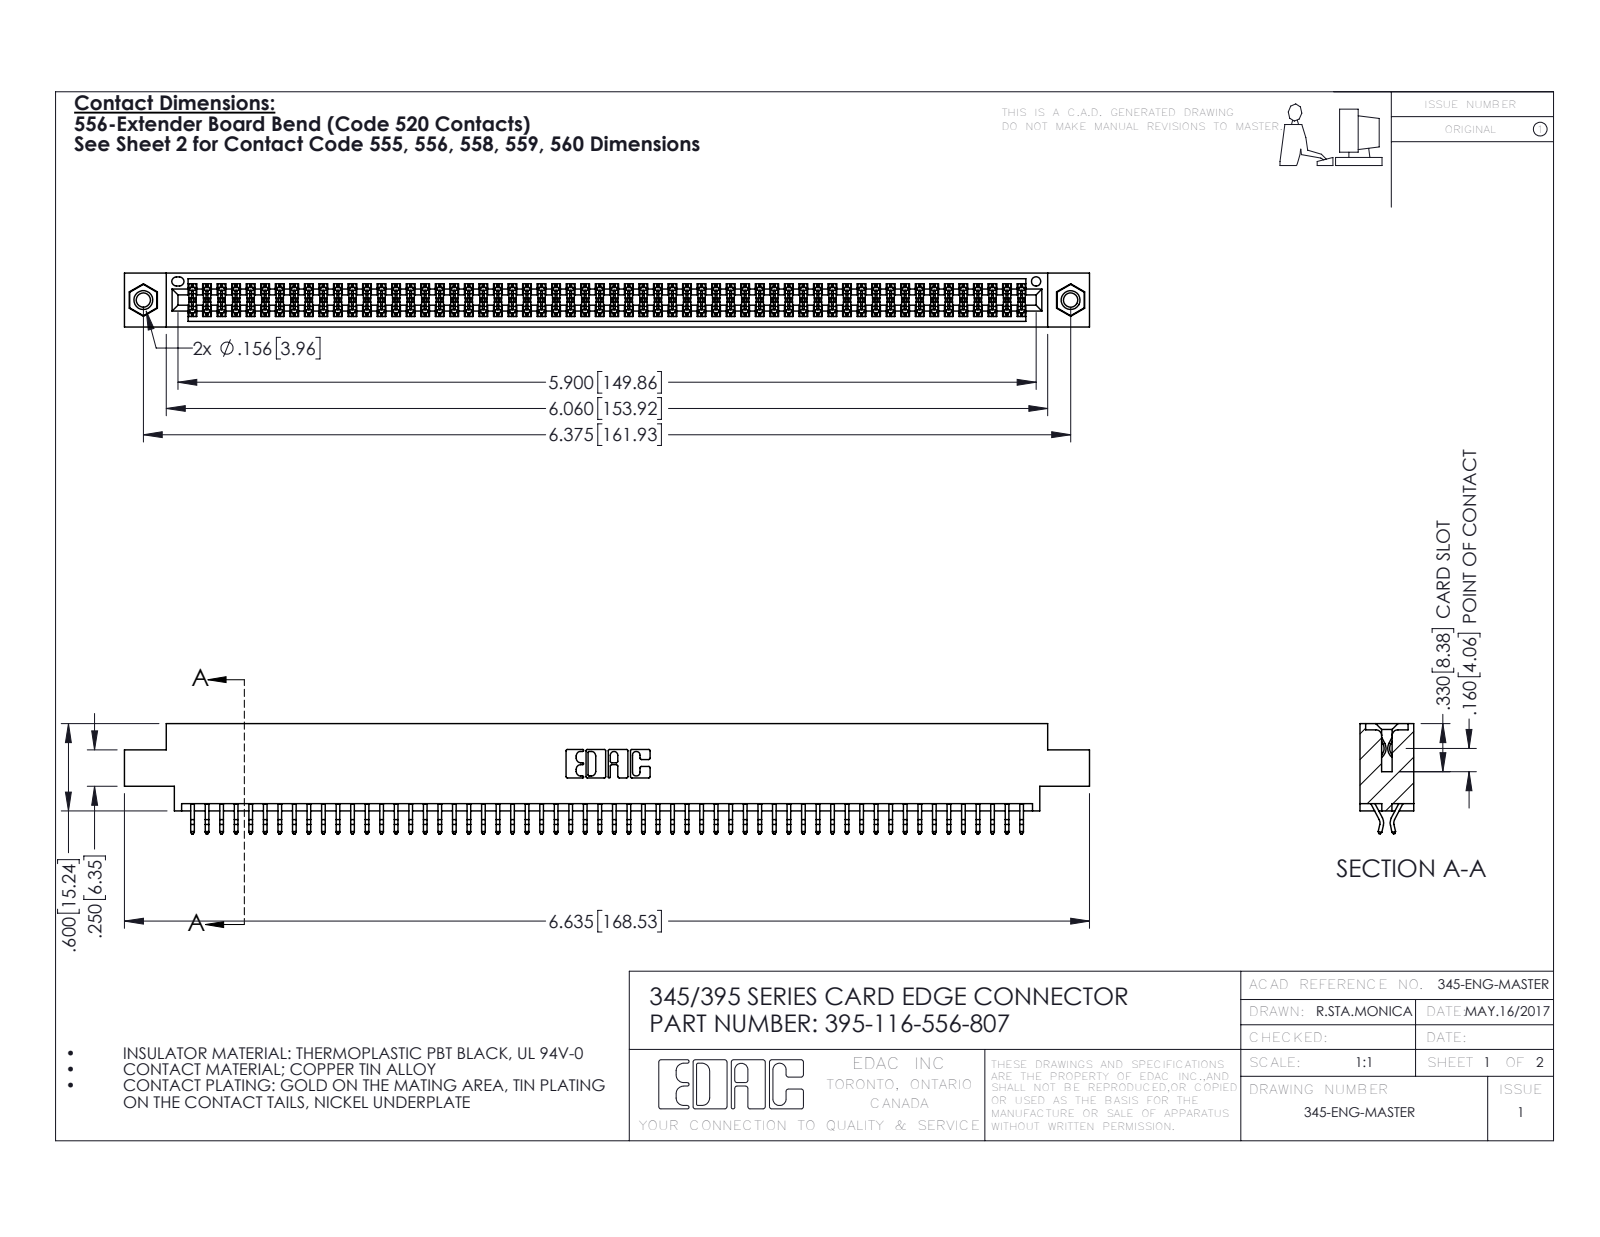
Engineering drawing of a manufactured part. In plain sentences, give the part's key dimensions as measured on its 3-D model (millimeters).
The part is named "395-116-556-807; 345-292-001_556 Tail; 345 Part_0.170 Offset - 0.156 Dia-TI; 345-250-001_345-250-005-103". Its 3-D file was written by "SolidWorks 2016 (CONFIG_CONTROL_DESIGN)". It is 119 solids with 6686 faces: 4408 planar, 2262 cylindrical and 16 other. Overall it measures 168.5 by 19.2 by 9.4 millimeters. Its volume is 16 390 cubic millimeters and its surface area 24 610 square millimeters. Round holes: 2 of diameter 2.5, 2 of diameter 3.2, 2 of diameter 4, 1 of diameter 1.6. Round bosses or shafts: 2 of diameter 3.9. Partial cylindrical surfaces (rounded edges, fillets, slot ends): 174 of radius 0.2, 22 of radius 0.3, 6 of radius 0.2, 6 of radius 0.8, 3 of radius 0.7, 2 of radius 0.3, 2 of radius 0.4, 2 of radius 0.5. The main face-to-face distances are 1.8, 7.6, 9.4, 5.1, 0.6, 2.5, 6.9, 5.7, 4.4, 3.8. The hole center spacings are 6.9, 155.9, 161.9.
